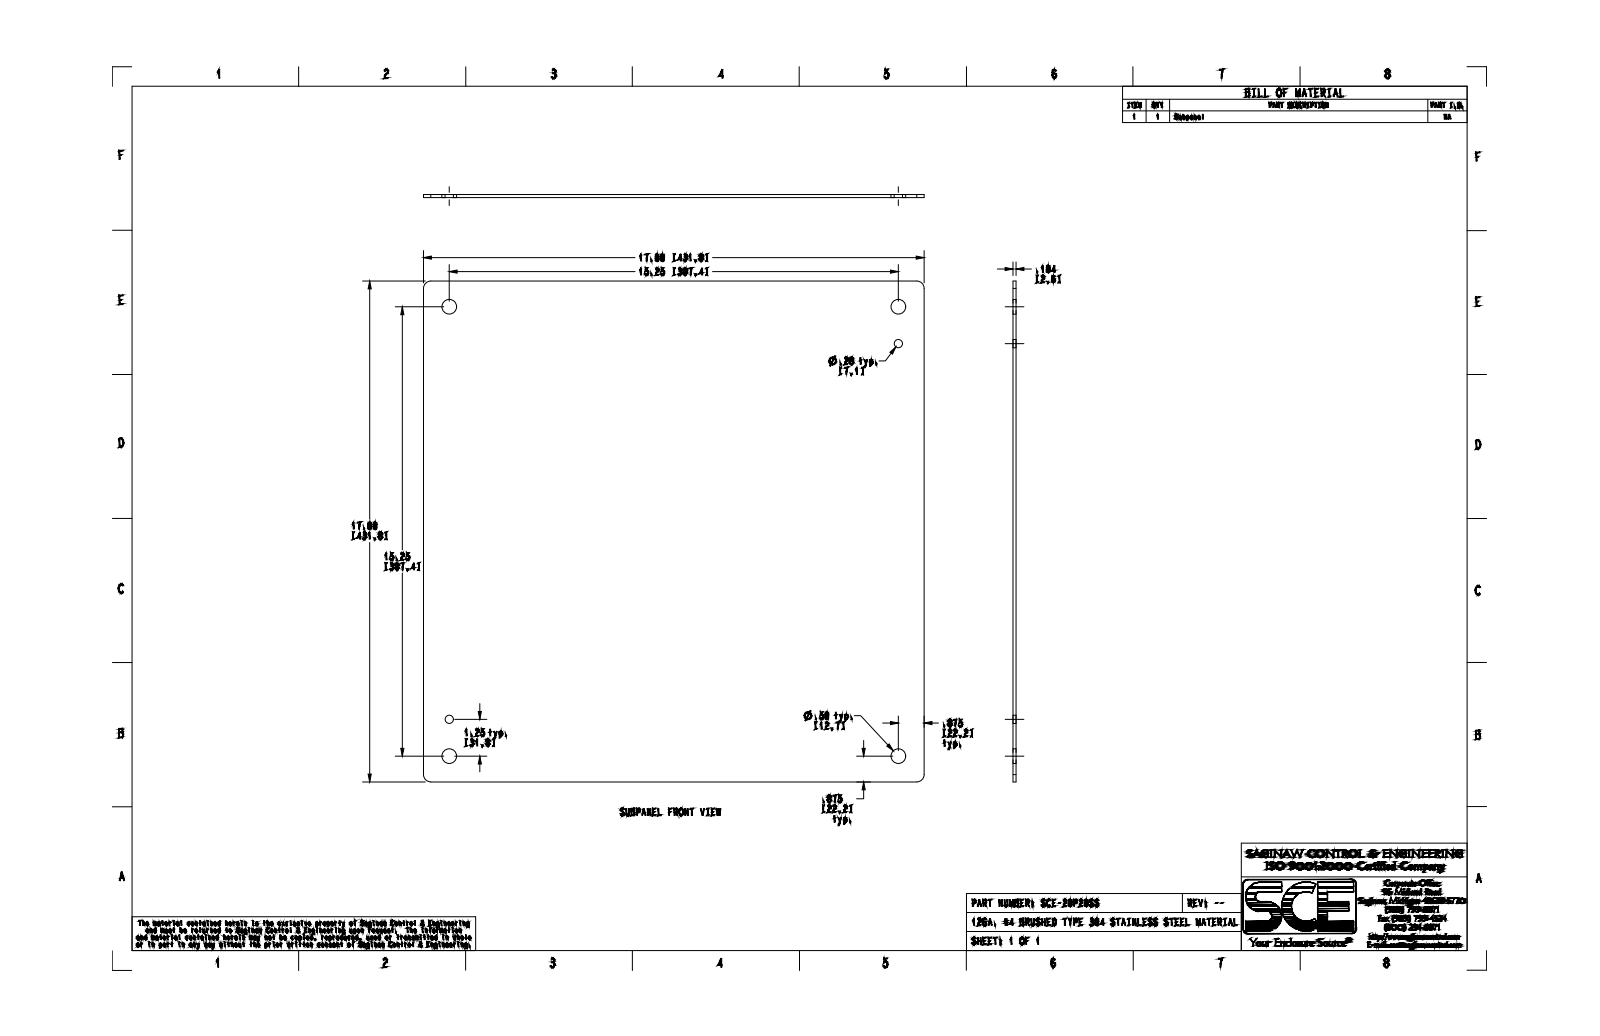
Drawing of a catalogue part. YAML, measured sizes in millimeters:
part_name: "SCE-20P20SS"
step_written_by: "SolidWorks 2019 (CONFIG_CONTROL_DESIGN)"
units: millimeters
bodies: {solids: 1, faces: 22, planar: 6, cylindrical: 0, other: 16}
overall_size: [431.8, 431.8, 2.6]
volume: 491000
surface_area: 376700
face_to_face_distances: [2.6, 431.8]
